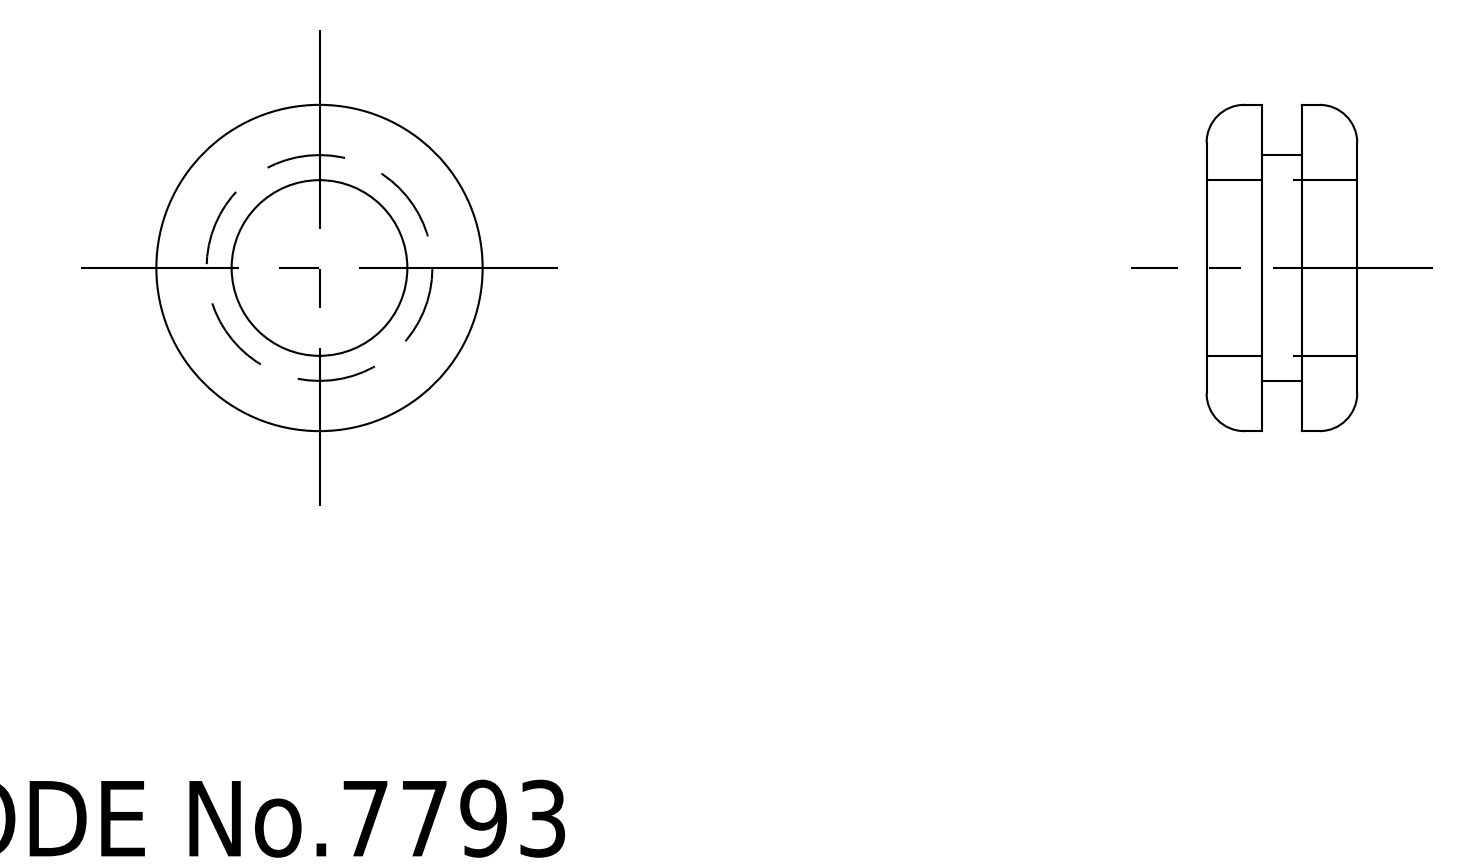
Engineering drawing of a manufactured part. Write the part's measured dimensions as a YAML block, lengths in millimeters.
part_name: "TM_346_8"
step_written_by: "SolidWorks 2015 (AUTOMOTIVE_DESIGN)"
units: millimeters
bodies: {solids: 1, faces: 16, planar: 4, cylindrical: 8, other: 4}
overall_size: [13, 13, 6]
volume: 417
surface_area: 629
round_holes:
  - {diameter: 7, count: 1}
round_bosses_or_shafts:
  - {diameter: 13, count: 1}
  - {diameter: 9, count: 1}
face_to_face_distances: [2.2, 3.8, 1.6, 6]
